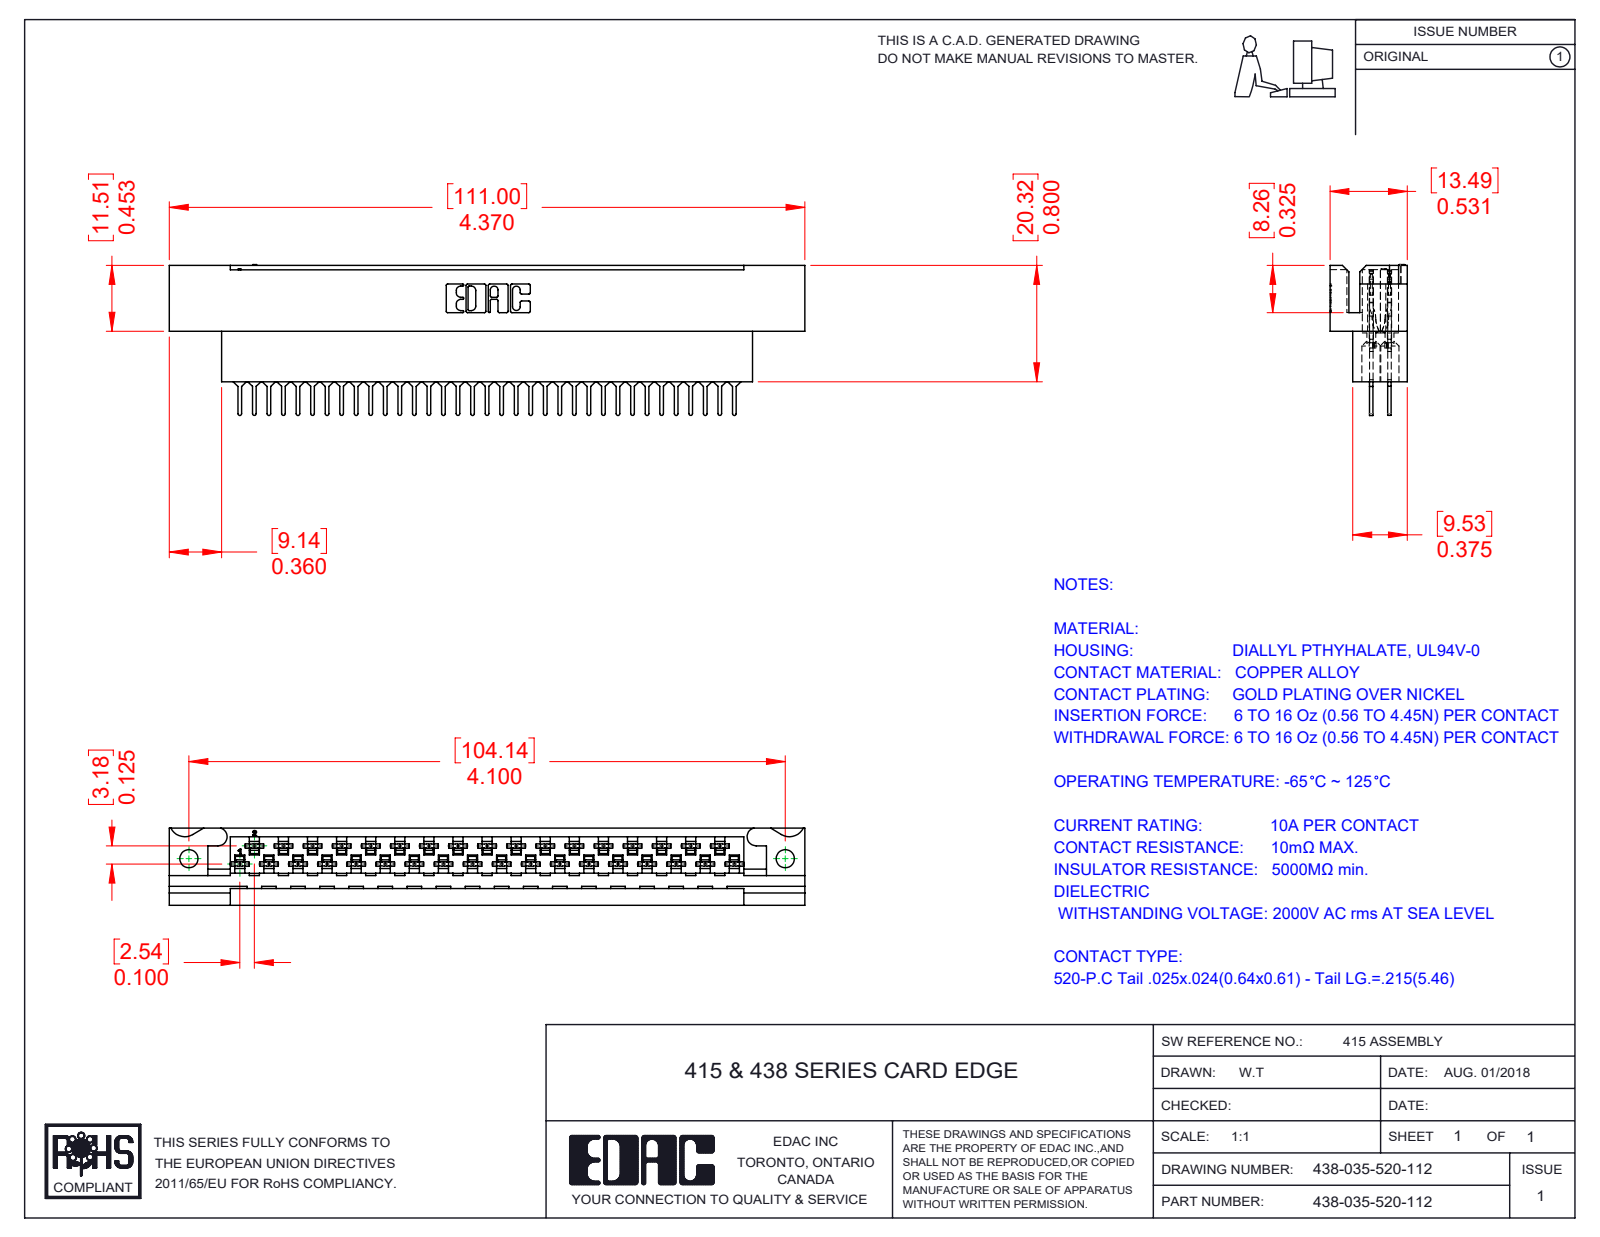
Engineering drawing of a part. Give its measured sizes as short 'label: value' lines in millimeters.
name: 438-035-520-112; 516-290-001_520; 438-210-001_438-210-035-112
written by: SolidWorks 2016 (CONFIG_CONTROL_DESIGN)
unit: mm
bodies: 36 solids, 3586 faces (2289 planar, 960 cylindrical, 337 other)
size: 111 × 26.32 × 13.49
volume: 18 143 mm³; area: 22 558 mm²
holes: 35× ⌀1.27, 35× ⌀3.3, 1× ⌀3.17, 1× ⌀3.18
rounds: 140× R0.3, 140× R0.56, 70× R0.18, 70× R0.2, 70× R0.41, 70× R2.03, 35× R0.32, 22× R0.25
face distances: 3.18, 1.88, 0.61, 1.27, 13.49, 2.92, 3.96, 7.49, 3.58, 6.61
hole spacings: 5.08, 10.16, 15.24, 20.32, 25.4, 30.48, 35.56, 2.54
